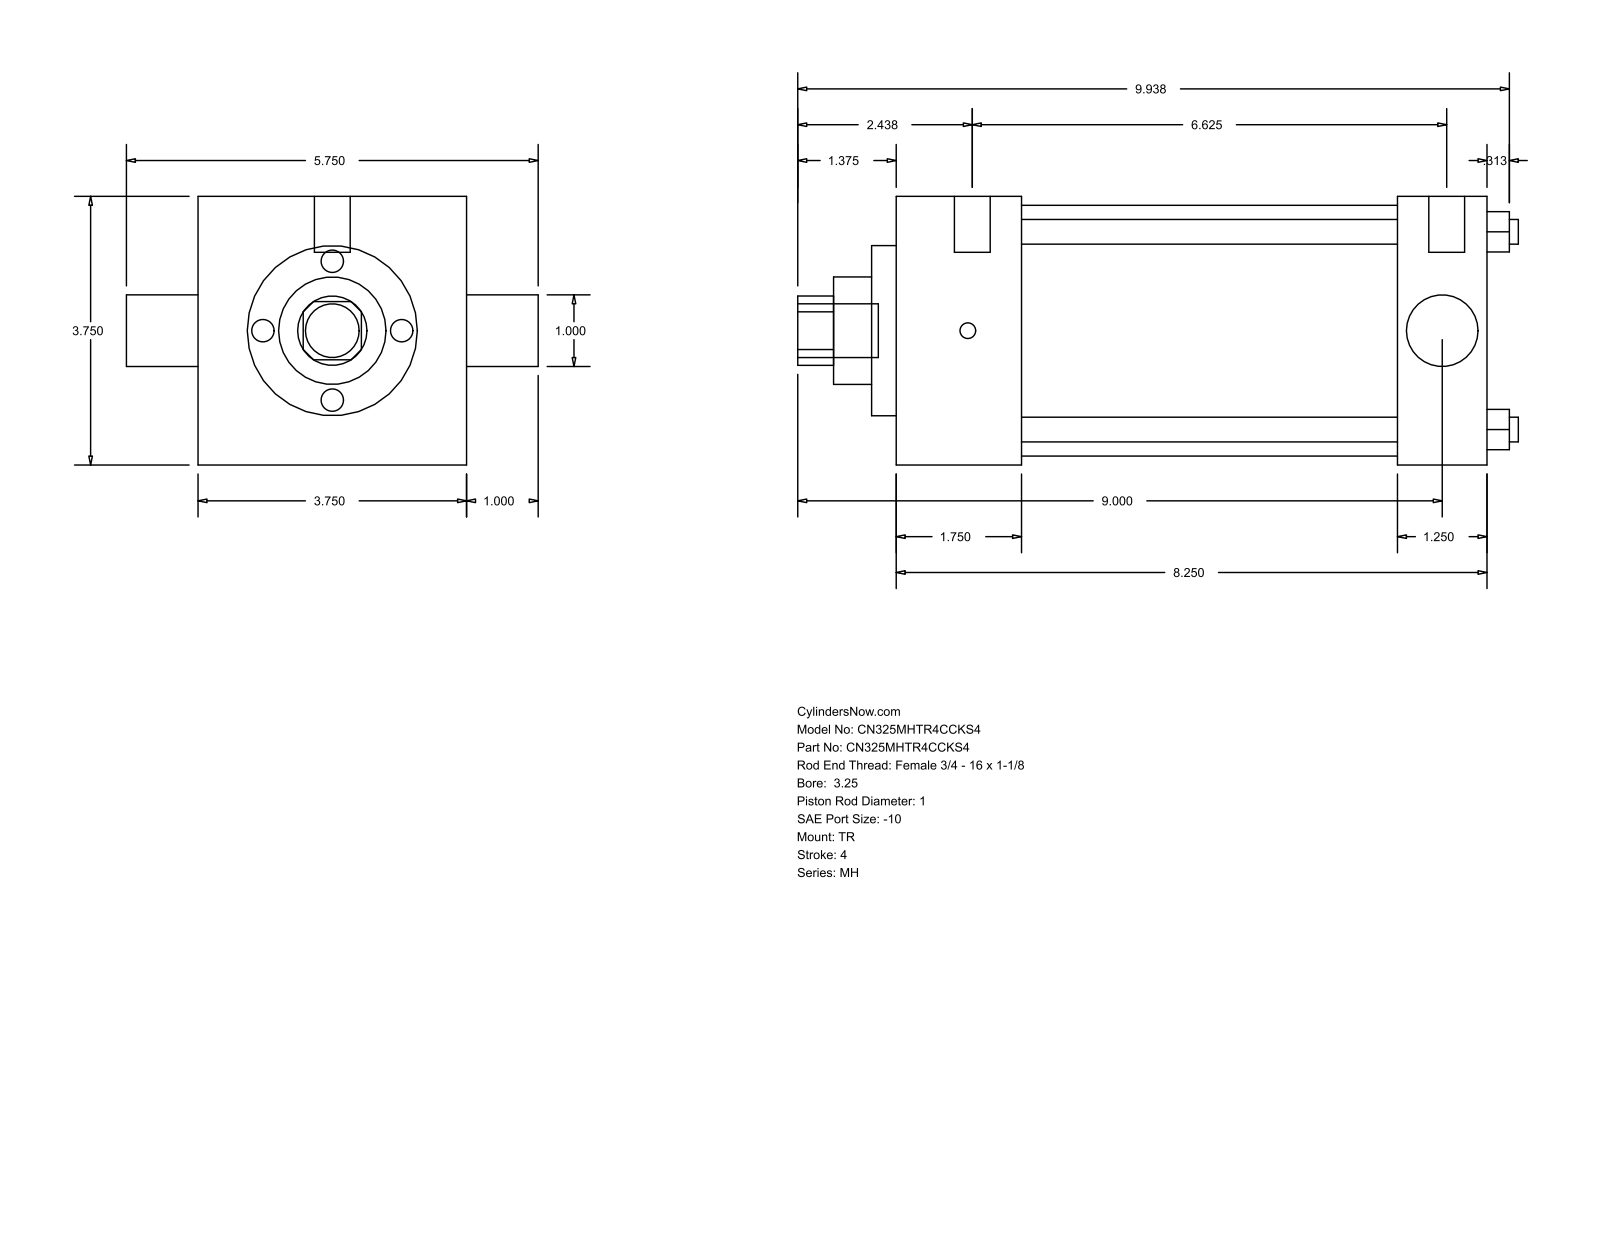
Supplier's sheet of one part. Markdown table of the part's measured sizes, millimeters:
| quantity | value |
| --- | --- |
| part name | MH_TR__0325_1 |
| STEP written by | GSSL Pune (CONFIG_CONTROL_DESIGN) |
| units | millimeters |
| bodies | 0 solids, 86 faces (61 planar, 25 cylindrical, 0 other) |
| overall size | 255.59 × 146.05 × 95.25 |
| round holes (diameter × count) | 8.76 × 4, 25.4 × 2, 38.1 × 1, 60.33 × 1, 88.9 × 1 |
| round bosses / shafts (diameter × count) | 5.56 × 3, 12.7 × 2, 19.05 × 1 |
| partial cylindrical surfaces (radius × count) | 12.29 × 1 |
| main face-to-face distances | 95.24, 209.55, 44.46, 177.8, 133.34, 165.09, 31.75, 8.73, 53.19, 186.53 |
| hole center spacings | 49.57, 70.1, 99.14 |
